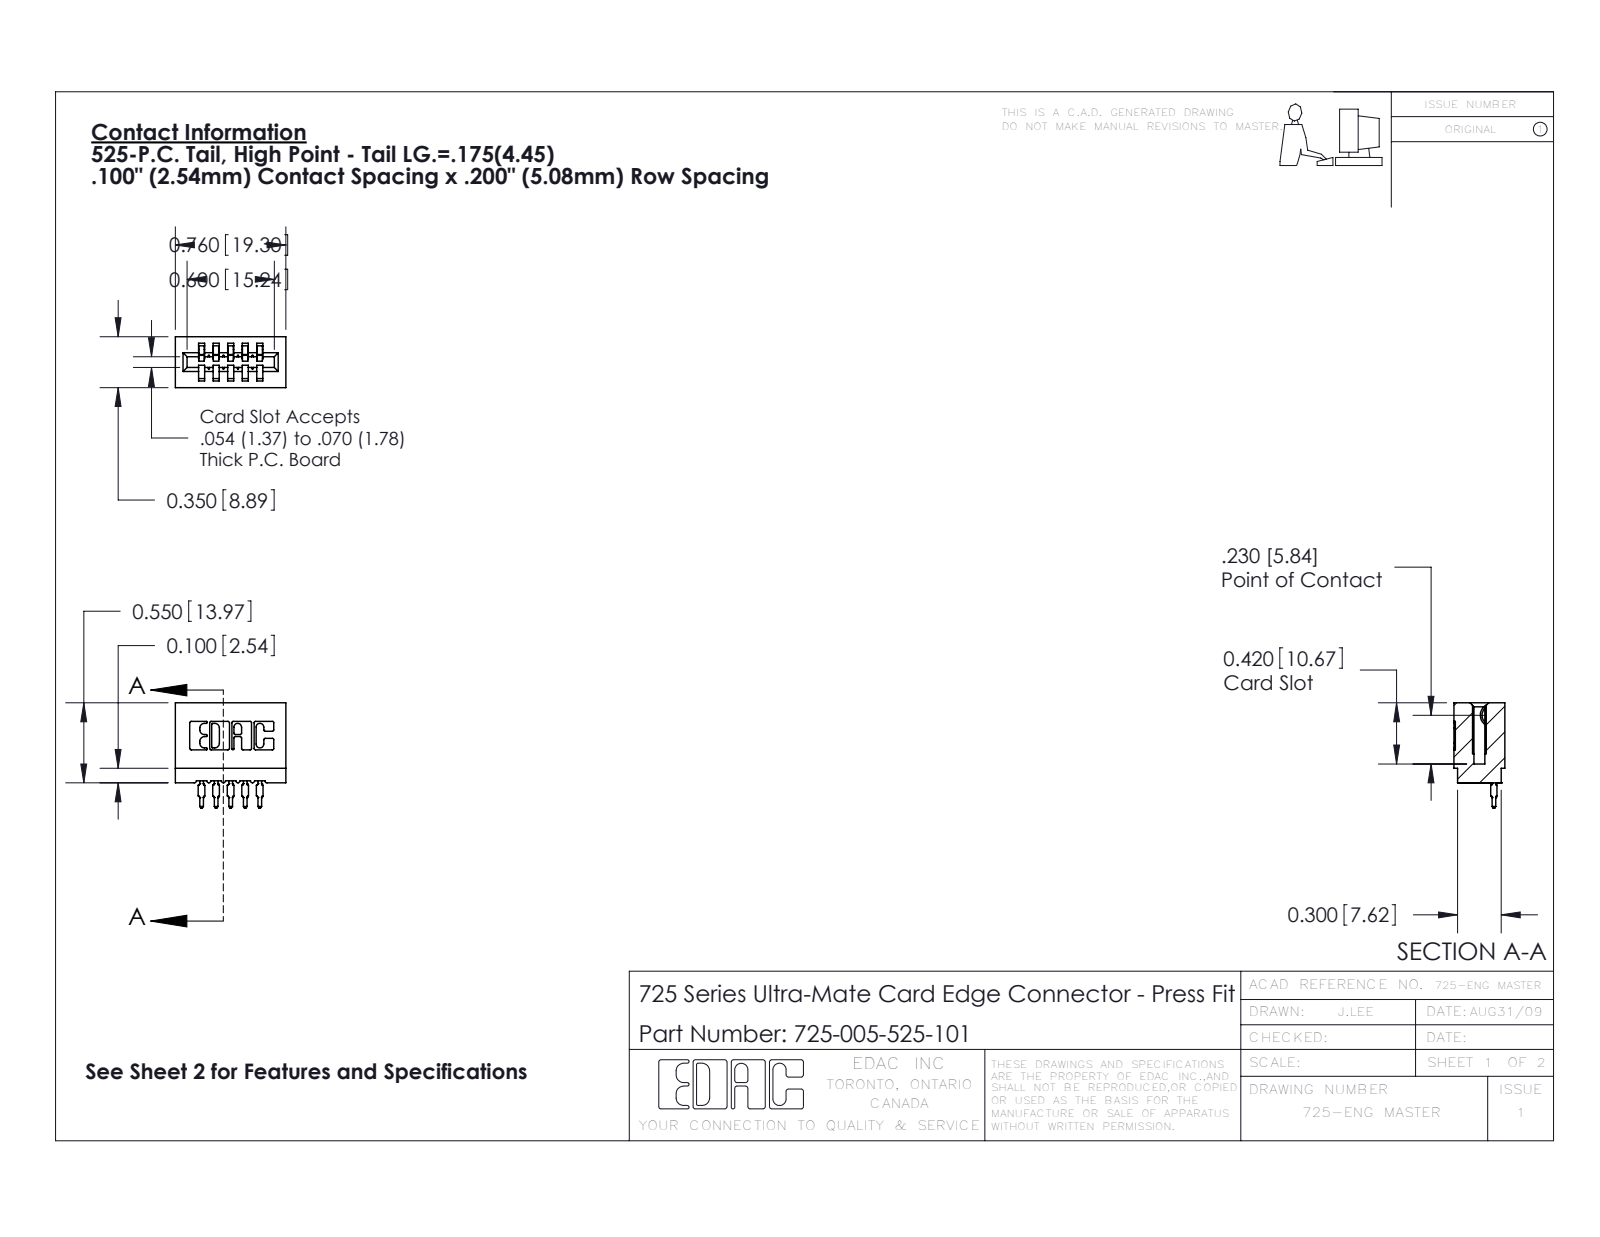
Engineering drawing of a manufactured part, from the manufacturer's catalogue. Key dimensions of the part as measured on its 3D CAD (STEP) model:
Part name (STEP PRODUCT): 745-292-001_525; 725-005-525-101; 725 Part_Insulator Option - 01
STEP written by: SolidWorks 2016 (CONFIG_CONTROL_DESIGN)
Units: inches
Bodies: 6 solids, 655 faces (390 planar, 135 cylindrical, 130 other)
Overall size (bounding box): 0.76 × 0.725 × 0.35
Volume: 0.102 in³ · Surface area: 3.912 in²
Partial cylindrical surfaces — rounded edges, fillets, slot ends (radius × count): R0.01 ×22, R0.015 ×10, R0.021 ×10, R0.007 ×6, R0.031 ×6, R0.005 ×4, R0.011 ×4, R0.026 ×3
Main face-to-face distances: 0.1, 0.2, 0.042, 0.058, 0.142, 0.3, 0.158, 0.242, 0.212, 0.35
